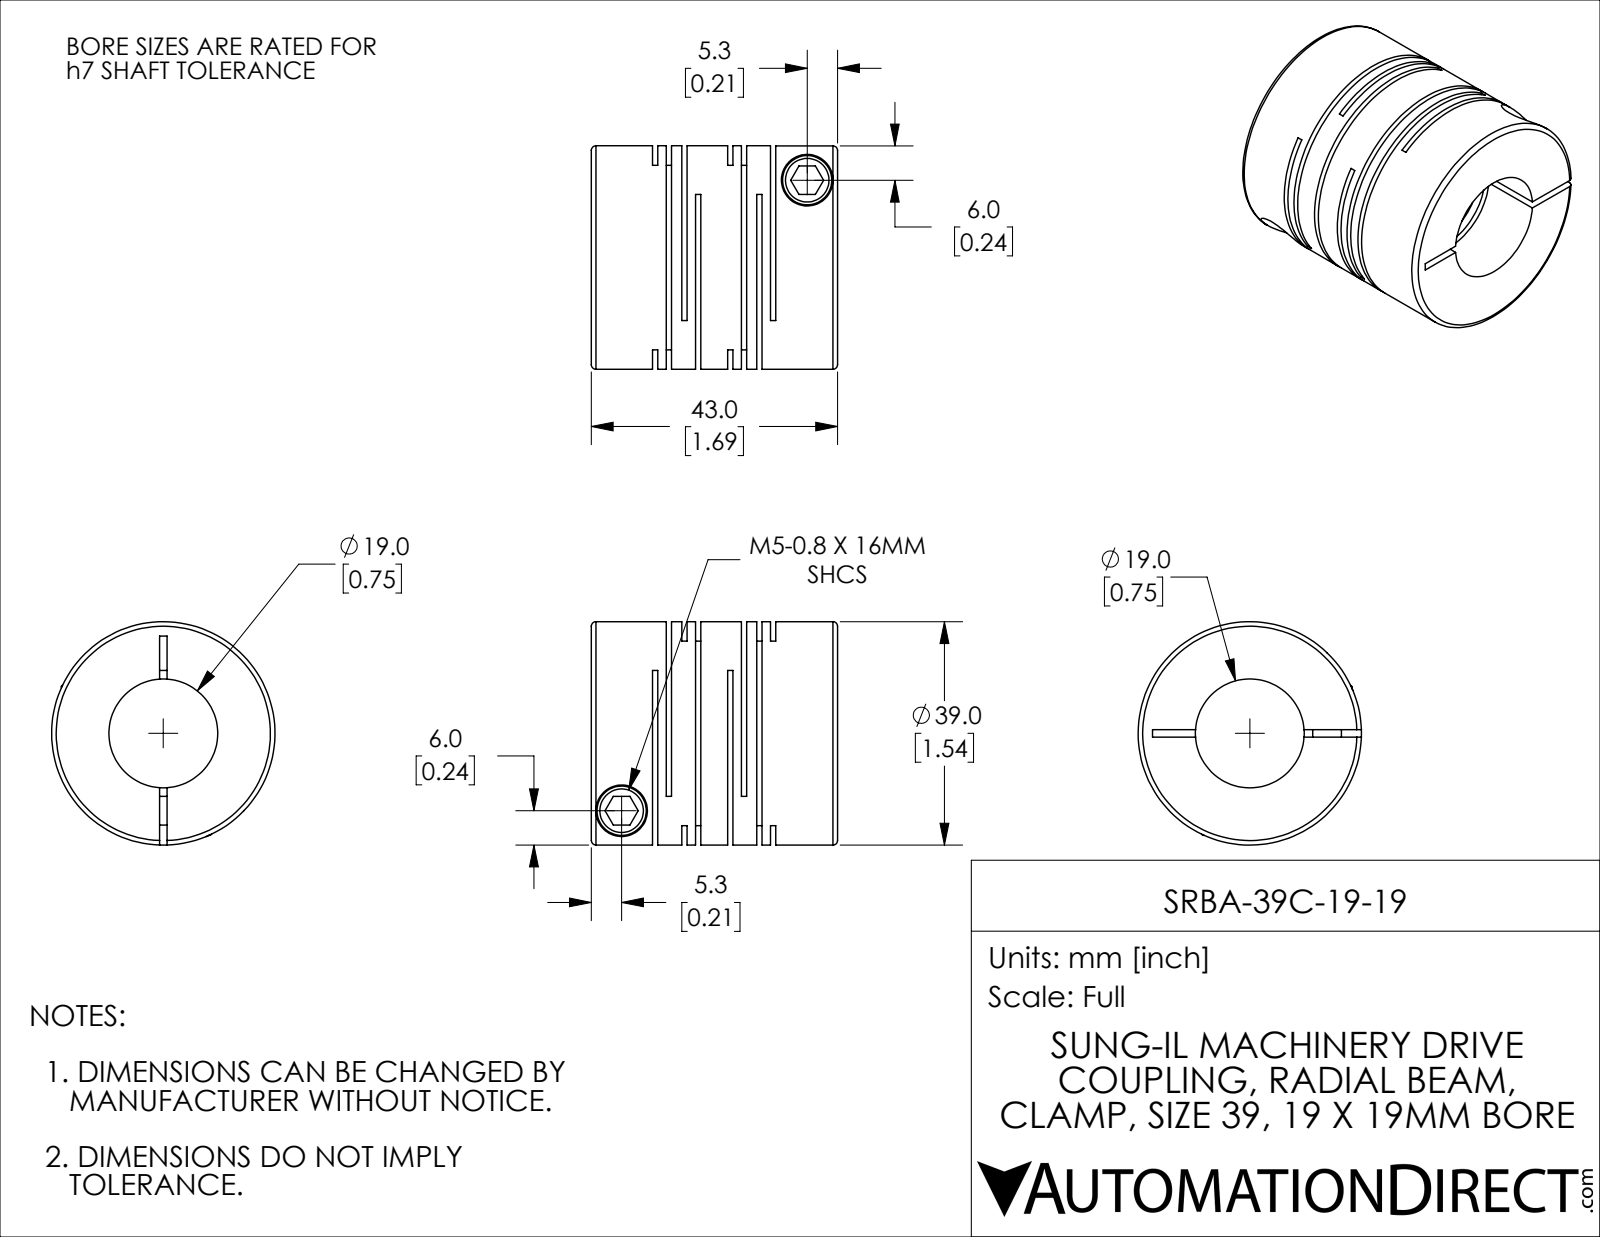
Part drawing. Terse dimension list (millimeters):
name: SRBA-39C-19-19
written by: SolidWorks 2021 (CONFIG_CONTROL_DESIGN)
unit: mm
bodies: 1 solid, 114 faces (60 planar, 42 cylindrical, 12 other)
size: 43 × 39 × 39
volume: 32 488 mm³; area: 21 674 mm²
holes: 2× ⌀5, 2× ⌀9, 1× ⌀19
bosses: 2× ⌀8.6, 1× ⌀39
face distances: 13.1, 0.92, 2.4, 5.1, 10.7, 14.02, 18.2, 1.48, 12.18, 4.18
